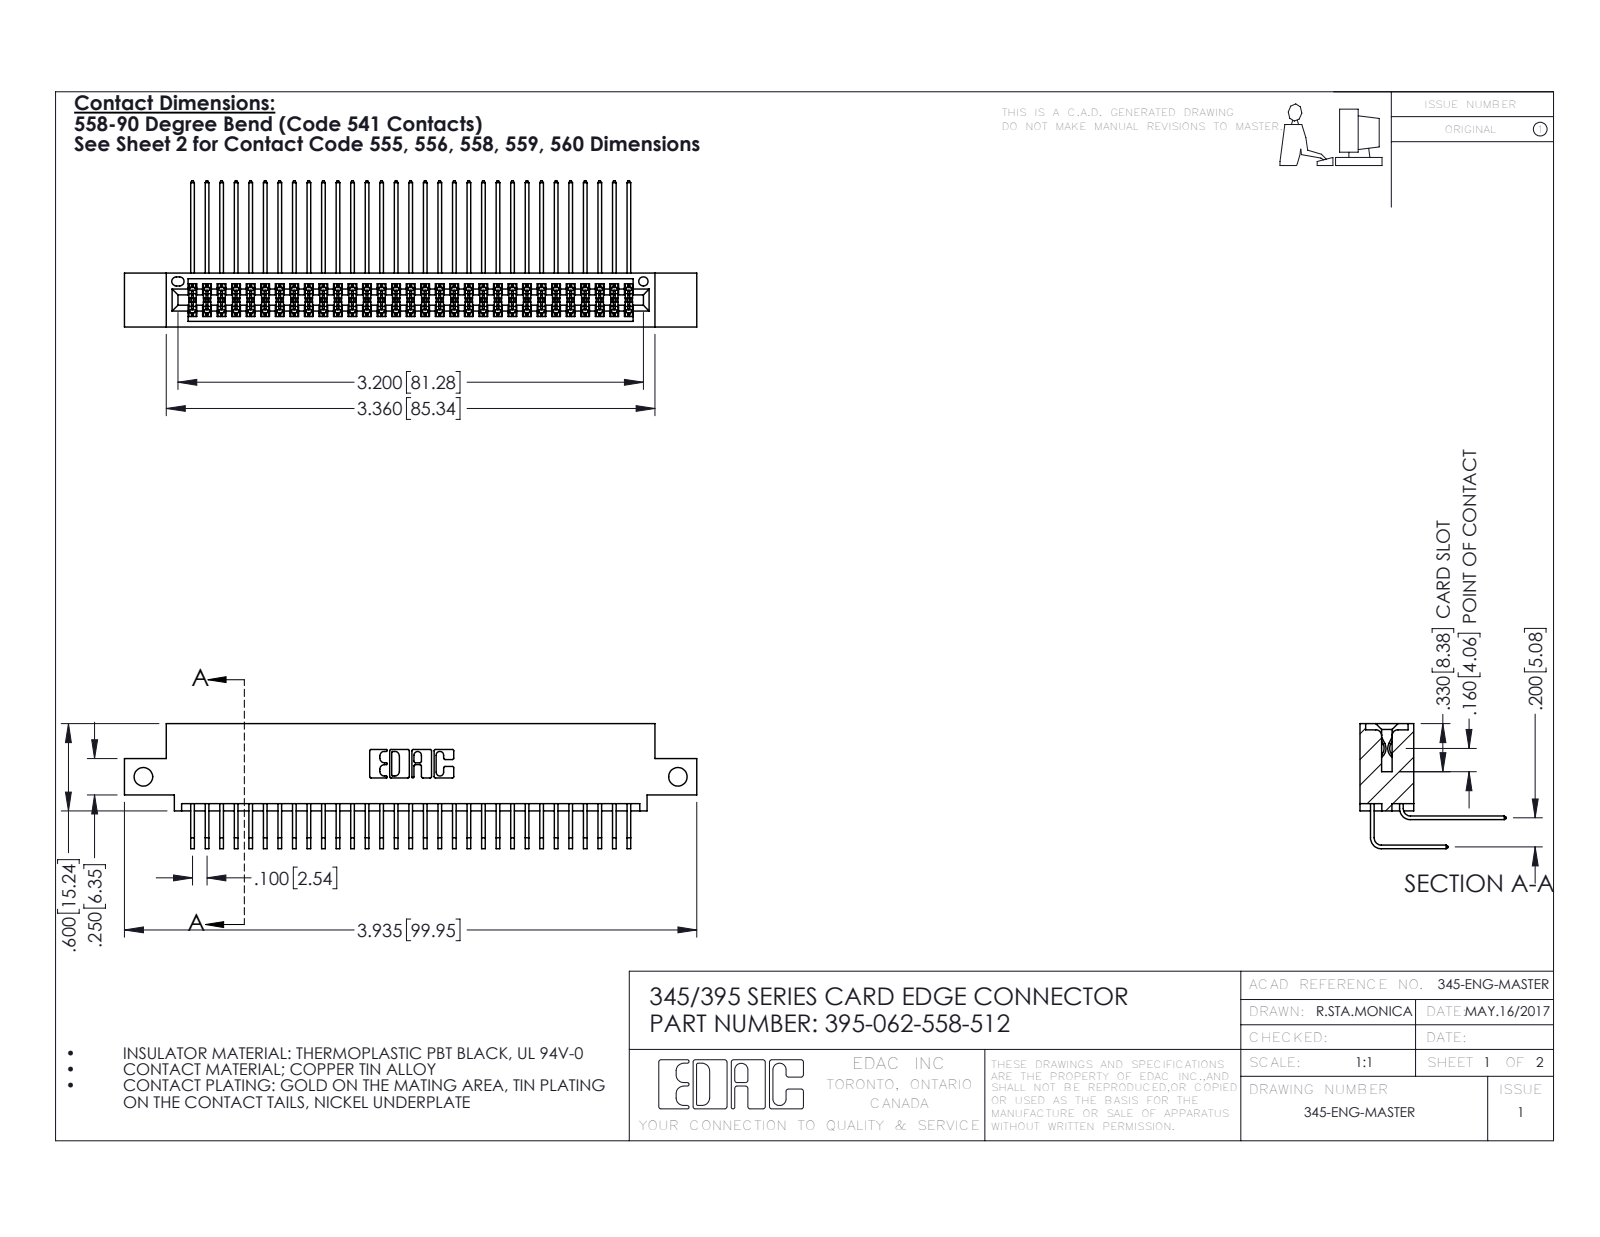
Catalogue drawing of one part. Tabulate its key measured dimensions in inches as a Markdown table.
| quantity | value |
| --- | --- |
| part name | 395-062-558-512; 345-292-001_558 559 Tail - 1; 345-292-001_558 Tail - 2; 345 Part_0.110 Offset - Side Mount |
| STEP written by | SolidWorks 2016 (CONFIG_CONTROL_DESIGN) |
| units | inches |
| bodies | 63 solids, 3354 faces (2254 planar, 1100 cylindrical, 0 other) |
| overall size | 3.935 × 1.005 × 0.859 |
| volume | 0.598 in³ |
| surface area | 24.67 in² |
| round holes (diameter × count) | 0.128 × 2, 0.064 × 1 |
| partial cylindrical surfaces (radius × count) | 0.006 × 94, 0.01 × 22, 0.007 × 6, 0.031 × 6, 0.026 × 3, 0.014 × 2, 0.019 × 2, 0.022 × 2 |
| main face-to-face distances | 0.072, 0.298, 0.2, 0.37, 0.098, 0.272, 0.025, 0.225, 0.025, 0.175 |
| hole center spacings | 3.675 |
